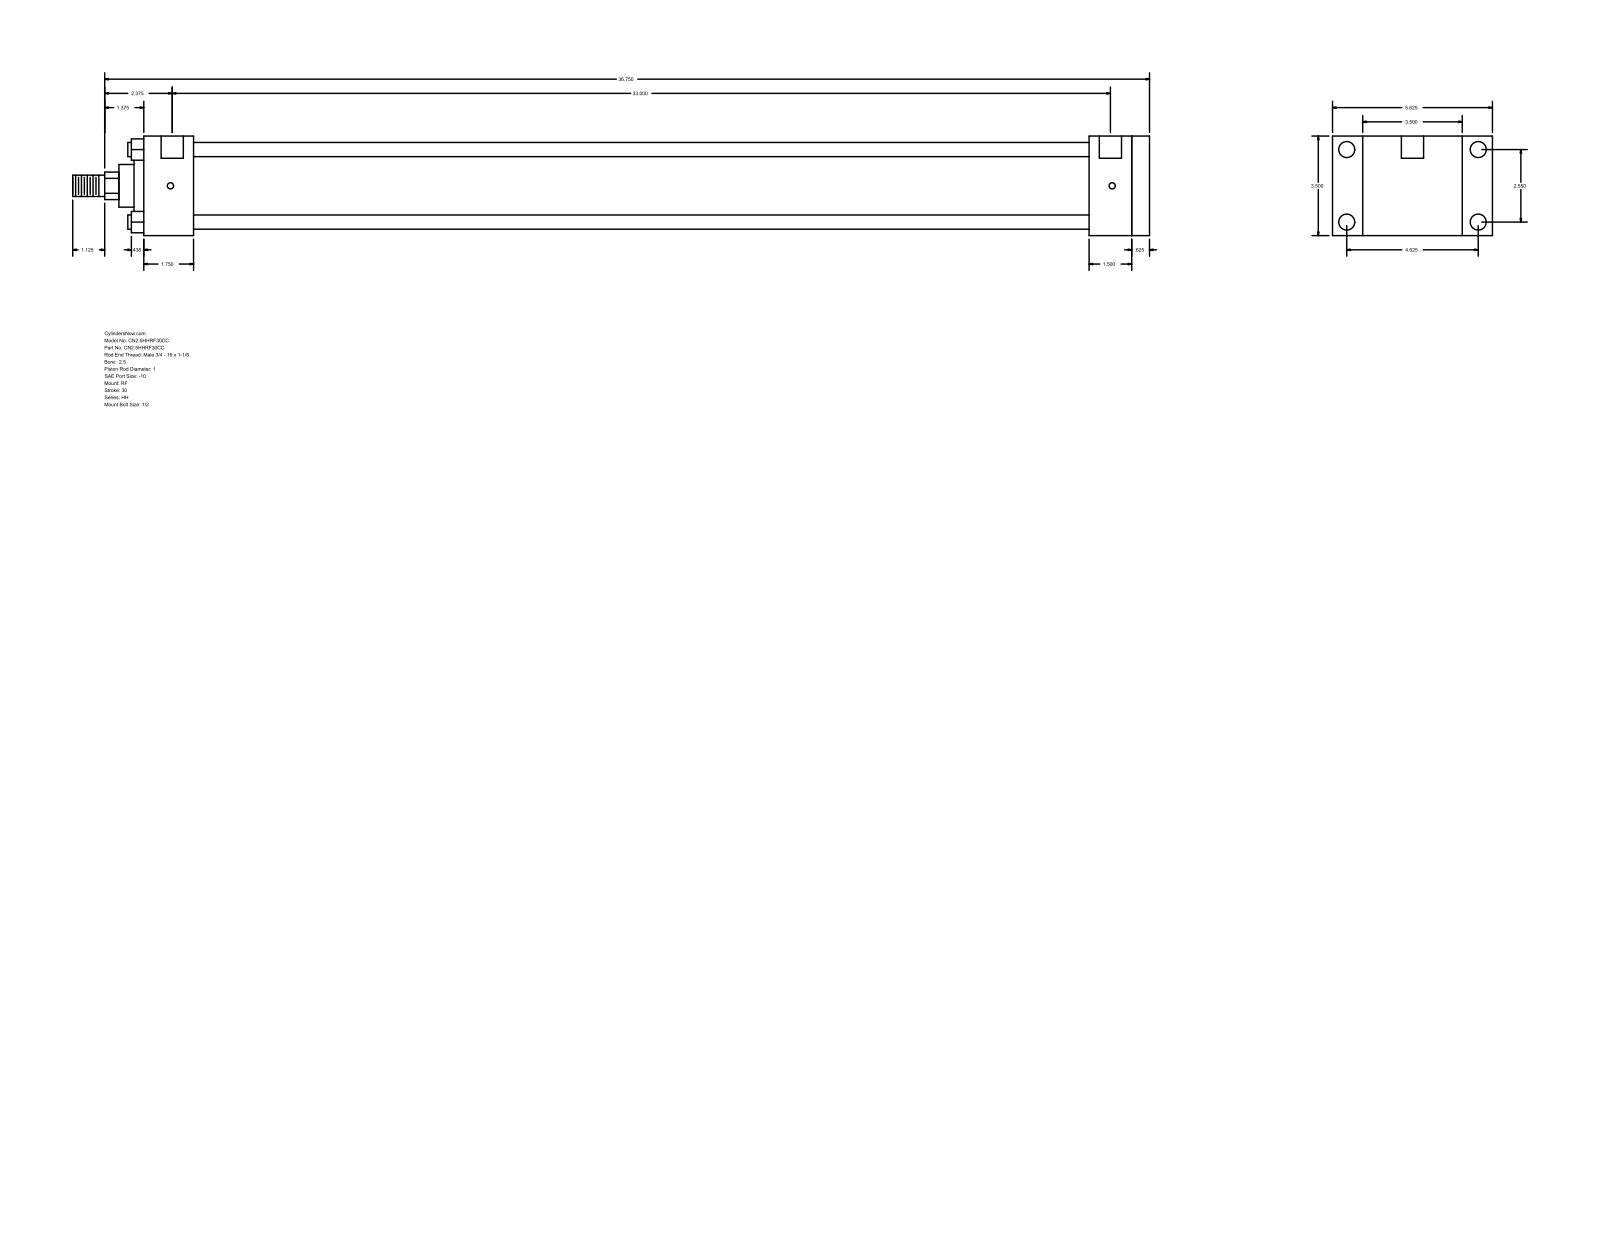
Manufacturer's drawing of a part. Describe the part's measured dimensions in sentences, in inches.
The part is named "HH_RF__0250_1". Its 3-D file was written by "GSSL Pune (CONFIG_CONTROL_DESIGN)". It is 0 solids with 94 faces: 65 planar, 29 cylindrical and 0 other. Overall it measures 37.875 by 5.625 by 3.5 inches. Round holes: 4 of diameter 0.219, 4 of diameter 0.563, 2 of diameter 0.781. Round bosses or shafts: 4 of diameter 0.5, 1 of diameter 2.875, 1 of diameter 2.375, 1 of diameter 1.5, 1 of diameter 1, 1 of diameter 0.75. Partial cylindrical surfaces (rounded edges, fillets, slot ends): 1 of radius 0.484. The main face-to-face distances are 3.5, 0.625, 34.75, 35.375, 1.5, 1.75, 33, 33.625, 33.25, 31.5. The hole center spacings are 0.063, 2.55, 4.625, 5.281, 33.062, 33.125, 33.
